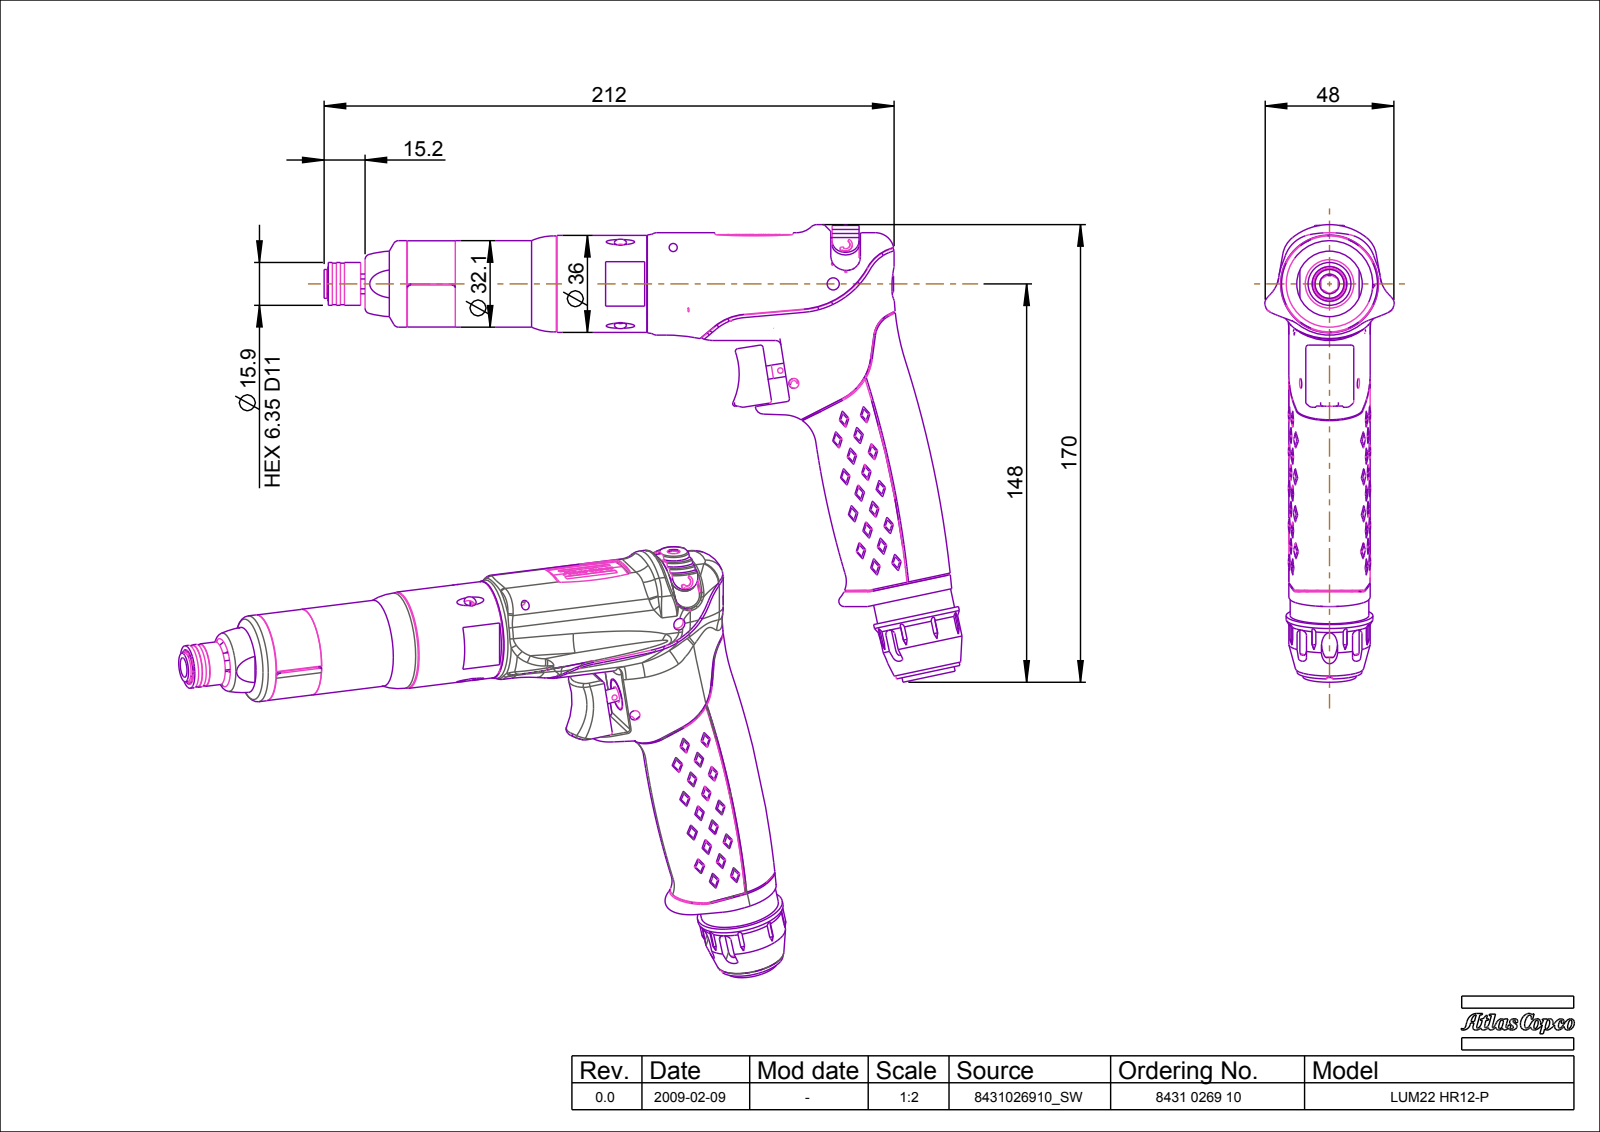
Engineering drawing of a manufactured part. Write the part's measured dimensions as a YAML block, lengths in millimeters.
part_name: "8431026910_SW"
step_written_by: "PRO/ENGINEER BY PARAMETRIC TECHNOLOGY CORPORATION, 2007370 (CONFIG_CONTROL_DESIGN)"
units: millimeters
bodies: {solids: 0, faces: 918, planar: 81, cylindrical: 173, other: 664}
overall_size: [236.81, 169.8, 48.06]
round_holes:
  - {diameter: 4.5, count: 3}
  - {diameter: 3, count: 1}
  - {diameter: 7.3, count: 1}
  - {diameter: 7.5, count: 1}
  - {diameter: 11.4, count: 1}
  - {diameter: 11.45, count: 1}
  - {diameter: 26.4, count: 1}
round_bosses_or_shafts:
  - {diameter: 36, count: 1}
  - {diameter: 35.6, count: 1}
  - {diameter: 32.2, count: 1}
  - {diameter: 32.1, count: 1}
  - {diameter: 32, count: 1}
  - {diameter: 30.2, count: 1}
  - {diameter: 29.2, count: 1}
  - {diameter: 24.25, count: 1}
partial_cylinders:
  - {radius: 1, count: 10}
  - {radius: 0.75, count: 8}
  - {radius: 10, count: 4}
  - {radius: 3, count: 3}
  - {radius: 38, count: 3}
  - {radius: 1.5, count: 2}
  - {radius: 2.5, count: 2}
  - {radius: 5, count: 2}
face_to_face_distances: [1.5, 29.8, 32, 27.29, 57.09, 2.9, 30.19, 59.99, 6.34, 1.7]
hole_center_spacings: [60.91]
